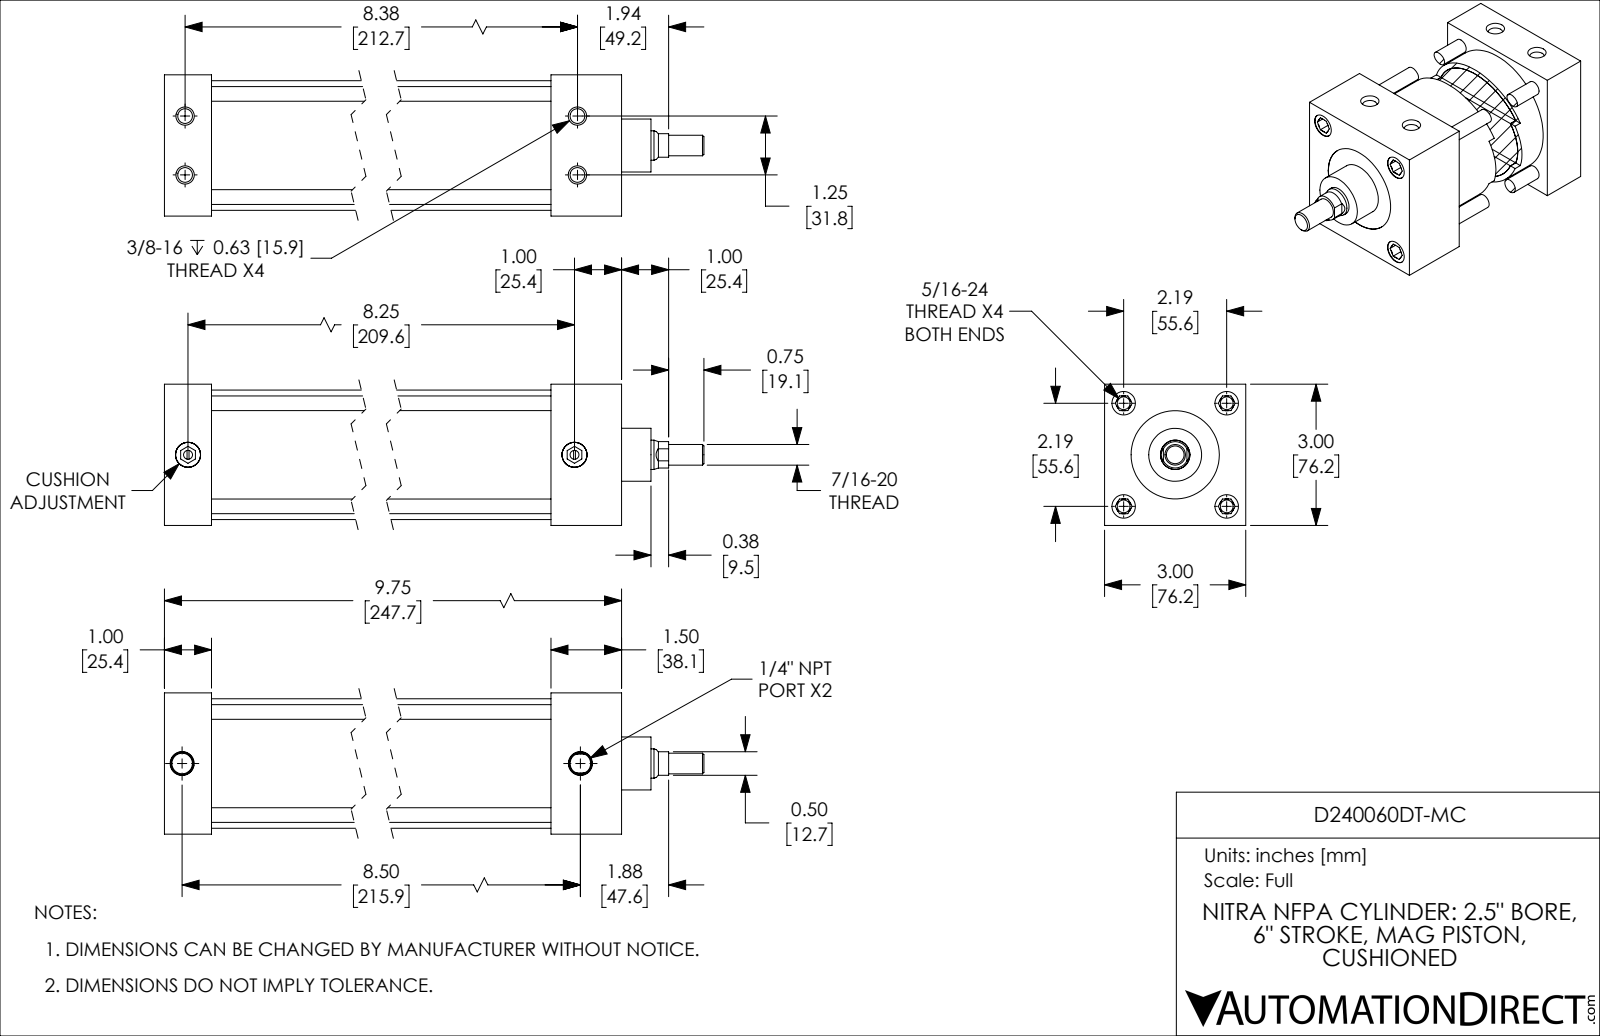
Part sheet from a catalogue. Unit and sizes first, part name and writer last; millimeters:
Units: millimetres
Overall size (bounding box): 292.1 × 76.2 × 76.2
Round holes (diameter × count): ⌀6.9 ×4, ⌀8 ×4, ⌀12.7 ×4, ⌀4.8 ×2, ⌀11.1 ×2, ⌀13.5 ×2, ⌀15.9 ×1, ⌀47.6 ×1, ⌀63.5 ×1
Round bosses / shafts (diameter × count): ⌀7.9 ×4, ⌀13.5 ×2, ⌀69.9 ×1, ⌀63.5 ×1, ⌀28.6 ×1, ⌀15.8 ×1, ⌀11.1 ×1
Partial cylindrical surfaces — rounded edges, fillets, slot ends (radius × count): R7.1 ×1
Main face-to-face distances: 76.2, 25.4, 209.6, 184.2, 247.7, 222.3, 38.1, 31.8, 57.2, 152.4
Hole centre spacings: 39.3, 55.6, 214.9, 16, 16, 31.8, 78.7, 212.7
Volume: 653 200 mm³ · Surface area: 173 200 mm²
Bodies: 4 solids, 248 faces (90 planar, 78 cylindrical, 80 other)
Part name (STEP PRODUCT): D240060DT-MC; D240060DT-MC_PISTON_KK1; D240060DT-MC_CUSHION; D240060DT-MC_BODY
STEP written by: SolidWorks 2019 (CONFIG_CONTROL_DESIGN)
